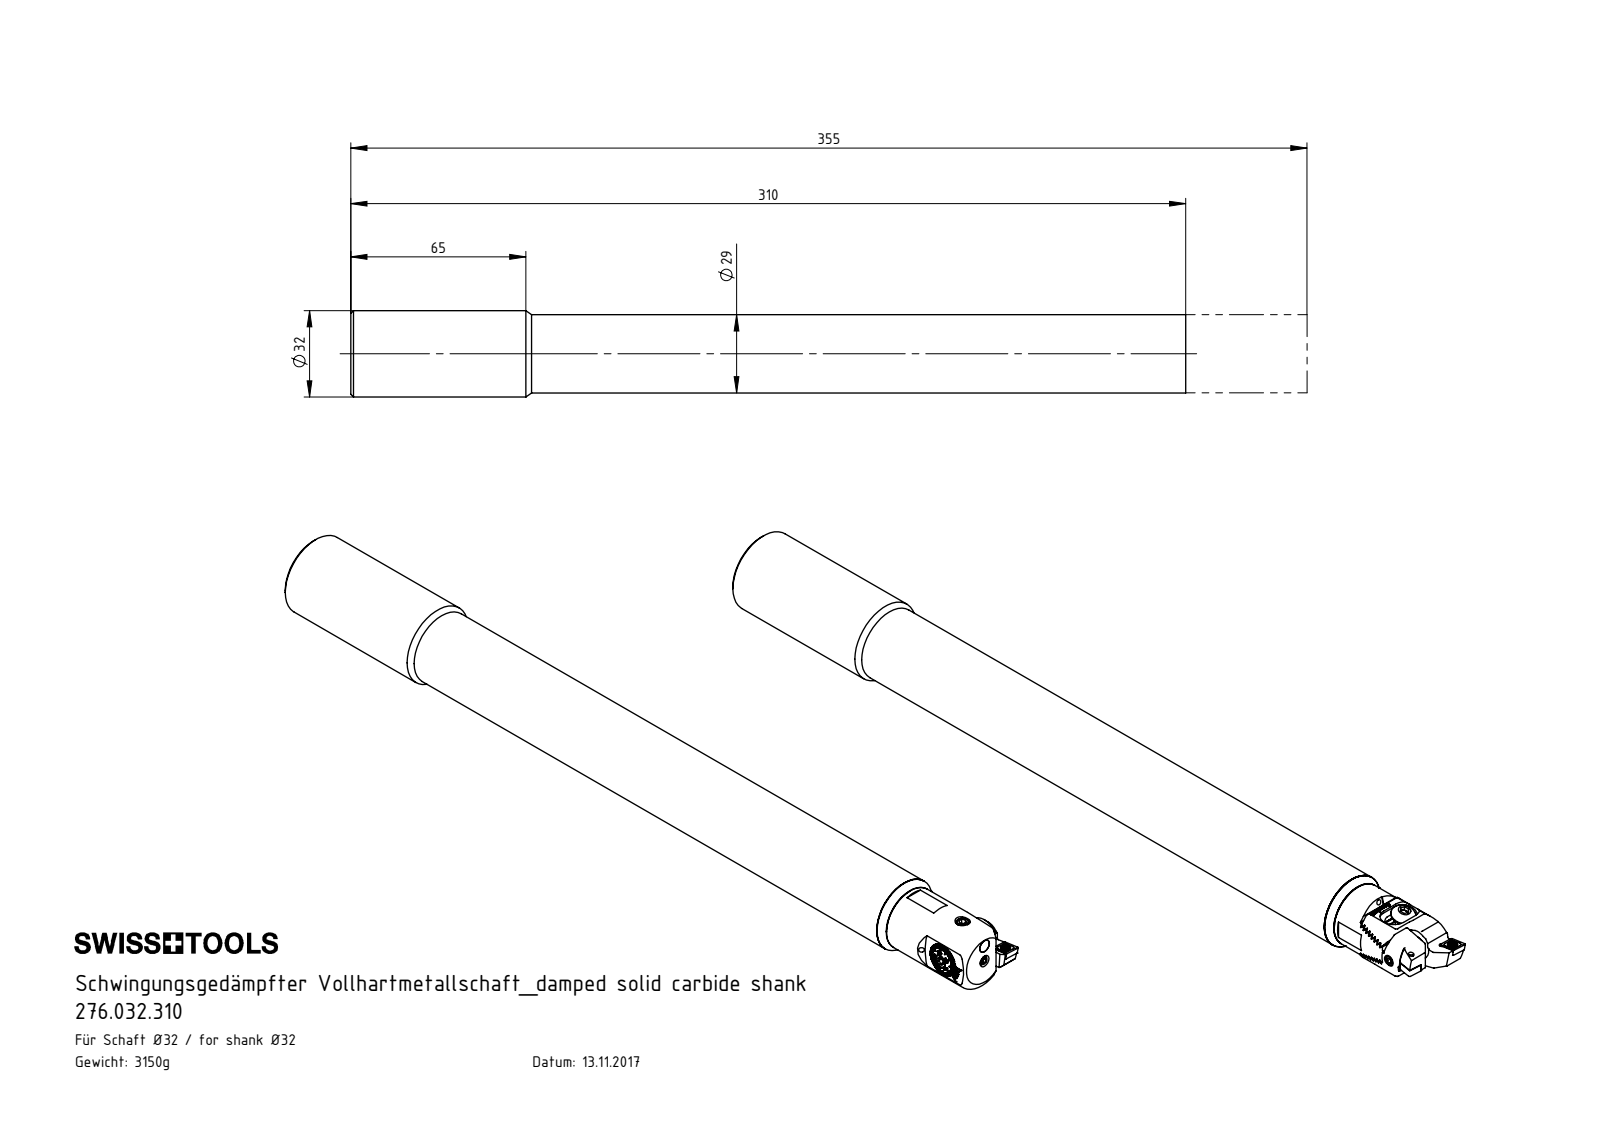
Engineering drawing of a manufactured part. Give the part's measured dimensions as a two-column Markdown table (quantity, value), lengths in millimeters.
| quantity | value |
| --- | --- |
| part name | HP5-F25.031.045_A; U32-HP5.029.310_A; Klebstoff D5; 276.032.310 (+8 more) |
| STEP written by | SolidWorks 2017 (CONFIG_CONTROL_DESIGN) |
| units | millimeters |
| bodies | 23 solids, 913 faces (387 planar, 178 cylindrical, 348 other) |
| overall size | 355 × 32 × 32 |
| volume | 231 710 mm³ |
| surface area | 56 951 mm² |
| round holes (diameter × count) | 2 × 5, 4.2 × 3, 2.05 × 2, 2.1 × 1, 2.4 × 1, 2.7 × 1, 2.8 × 1, 3 × 1, 3.3 × 1, 3.85 × 1, 5 × 1, 5.5 × 1 |
| round bosses / shafts (diameter × count) | 5 × 2, 4.95 × 2, 2.5 × 2, 32 × 1, 29 × 1, 25 × 1, 16 × 1, 12.98 × 1 |
| partial cylindrical surfaces (radius × count) | 0.21 × 6, 0.36 × 5, 0.5 × 4, 1.32 × 2, 0.2 × 1, 0.36 × 1, 1.05 × 1, 1.25 × 1 |
| main face-to-face distances | 310, 3, 274, 36, 313, 39, 8, 15, 352.15, 78.15 |
| hole center spacings | 3.84, 3.99, 4.48, 6.8, 9.46, 16.65 |
